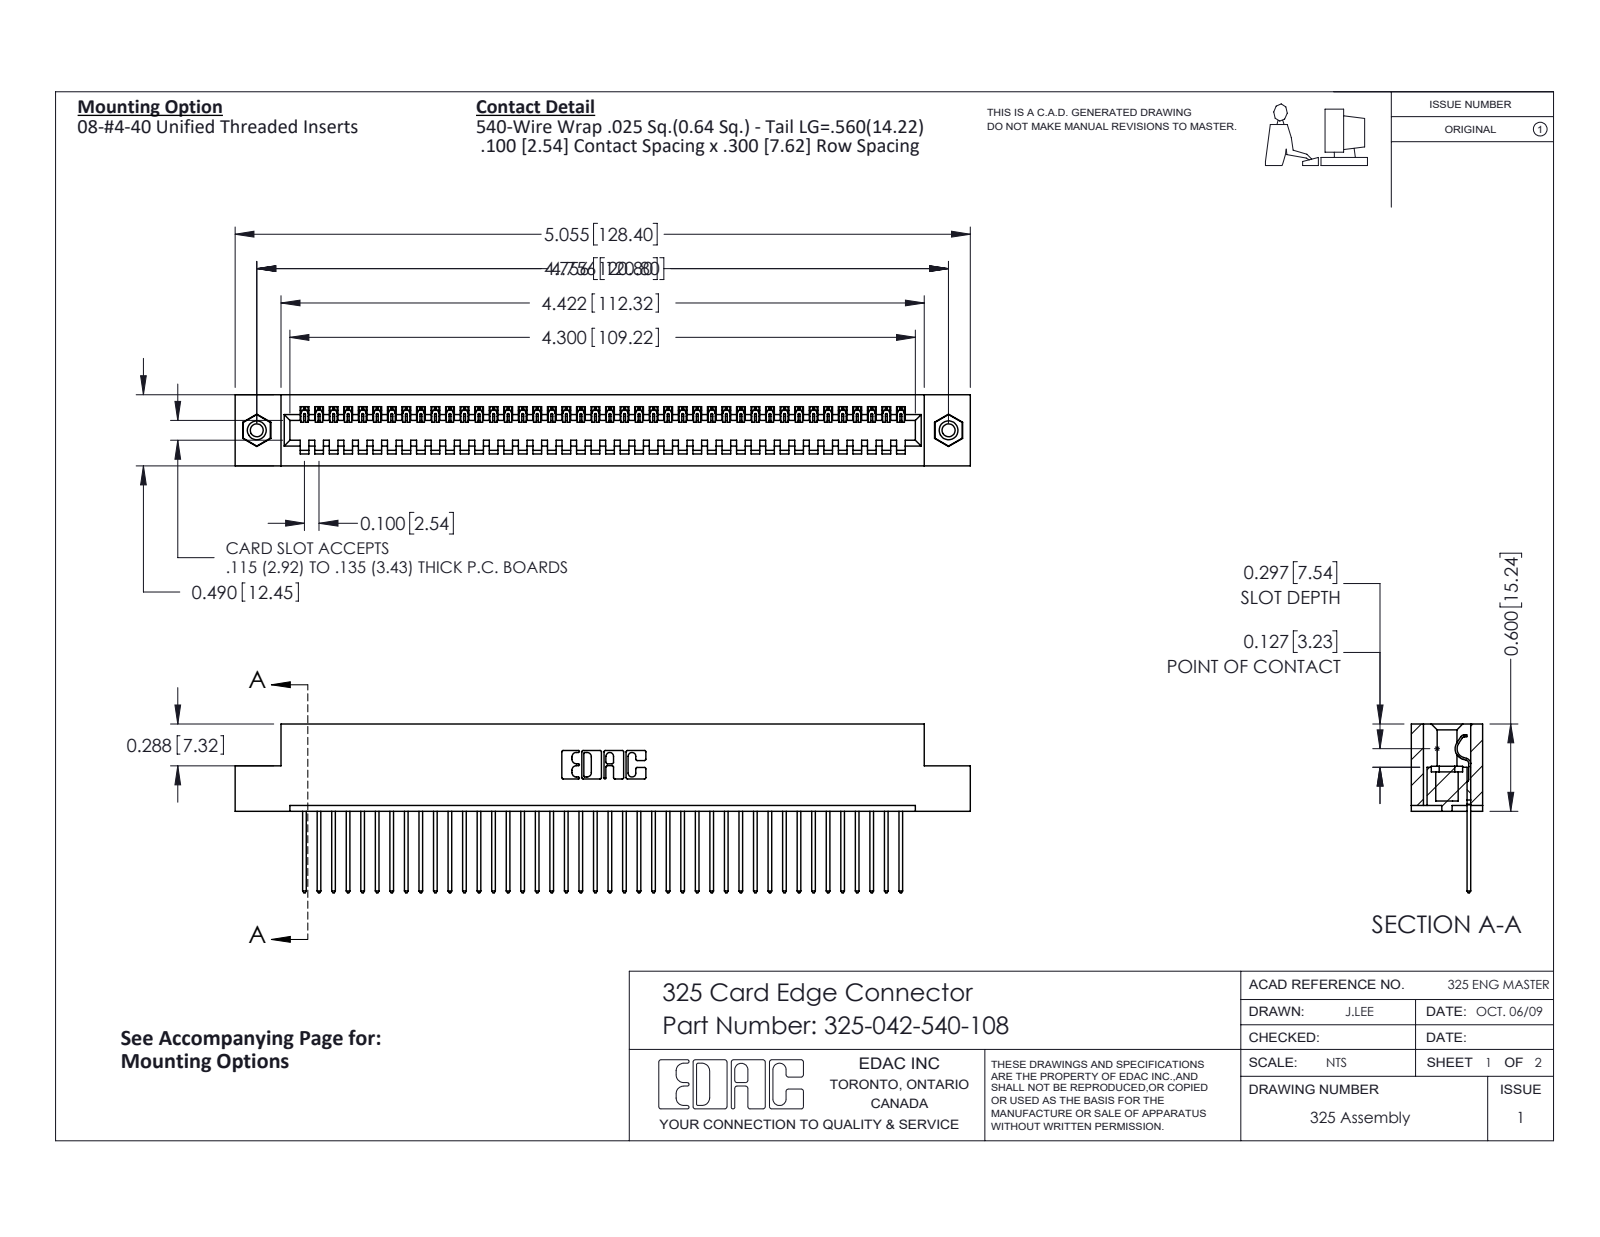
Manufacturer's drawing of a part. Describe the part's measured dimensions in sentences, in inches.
The part is named "325-292-001_325-293-140; 345-250-001_345-250-003-102; 325-042-540-108; 325 Part_TI". Its 3-D file was written by "SolidWorks 2016 (CONFIG_CONTROL_DESIGN)". It is 45 solids with 2610 faces: 1866 planar, 728 cylindrical and 16 other. Overall it measures 5.055 by 1.16 by 0.49 inches. Its volume is 0.998 cubic inches and its surface area 28.36 square inches. Round holes: 2 of diameter 0.089, 2 of diameter 0.125, 2 of diameter 0.16. Round bosses or shafts: 2 of diameter 0.155. Partial cylindrical surfaces (rounded edges, fillets, slot ends): 84 of radius 0.006, 84 of radius 0.01, 22 of radius 0.01, 6 of radius 0.007, 6 of radius 0.031, 3 of radius 0.026, 1 of radius 0.014, 1 of radius 0.022. The main face-to-face distances are 0.083, 0.407, 0.49, 0.3, 0.107, 0.383, 0.025, 0.325, 0.56, 0.04. The hole center spacings are 4.756.
